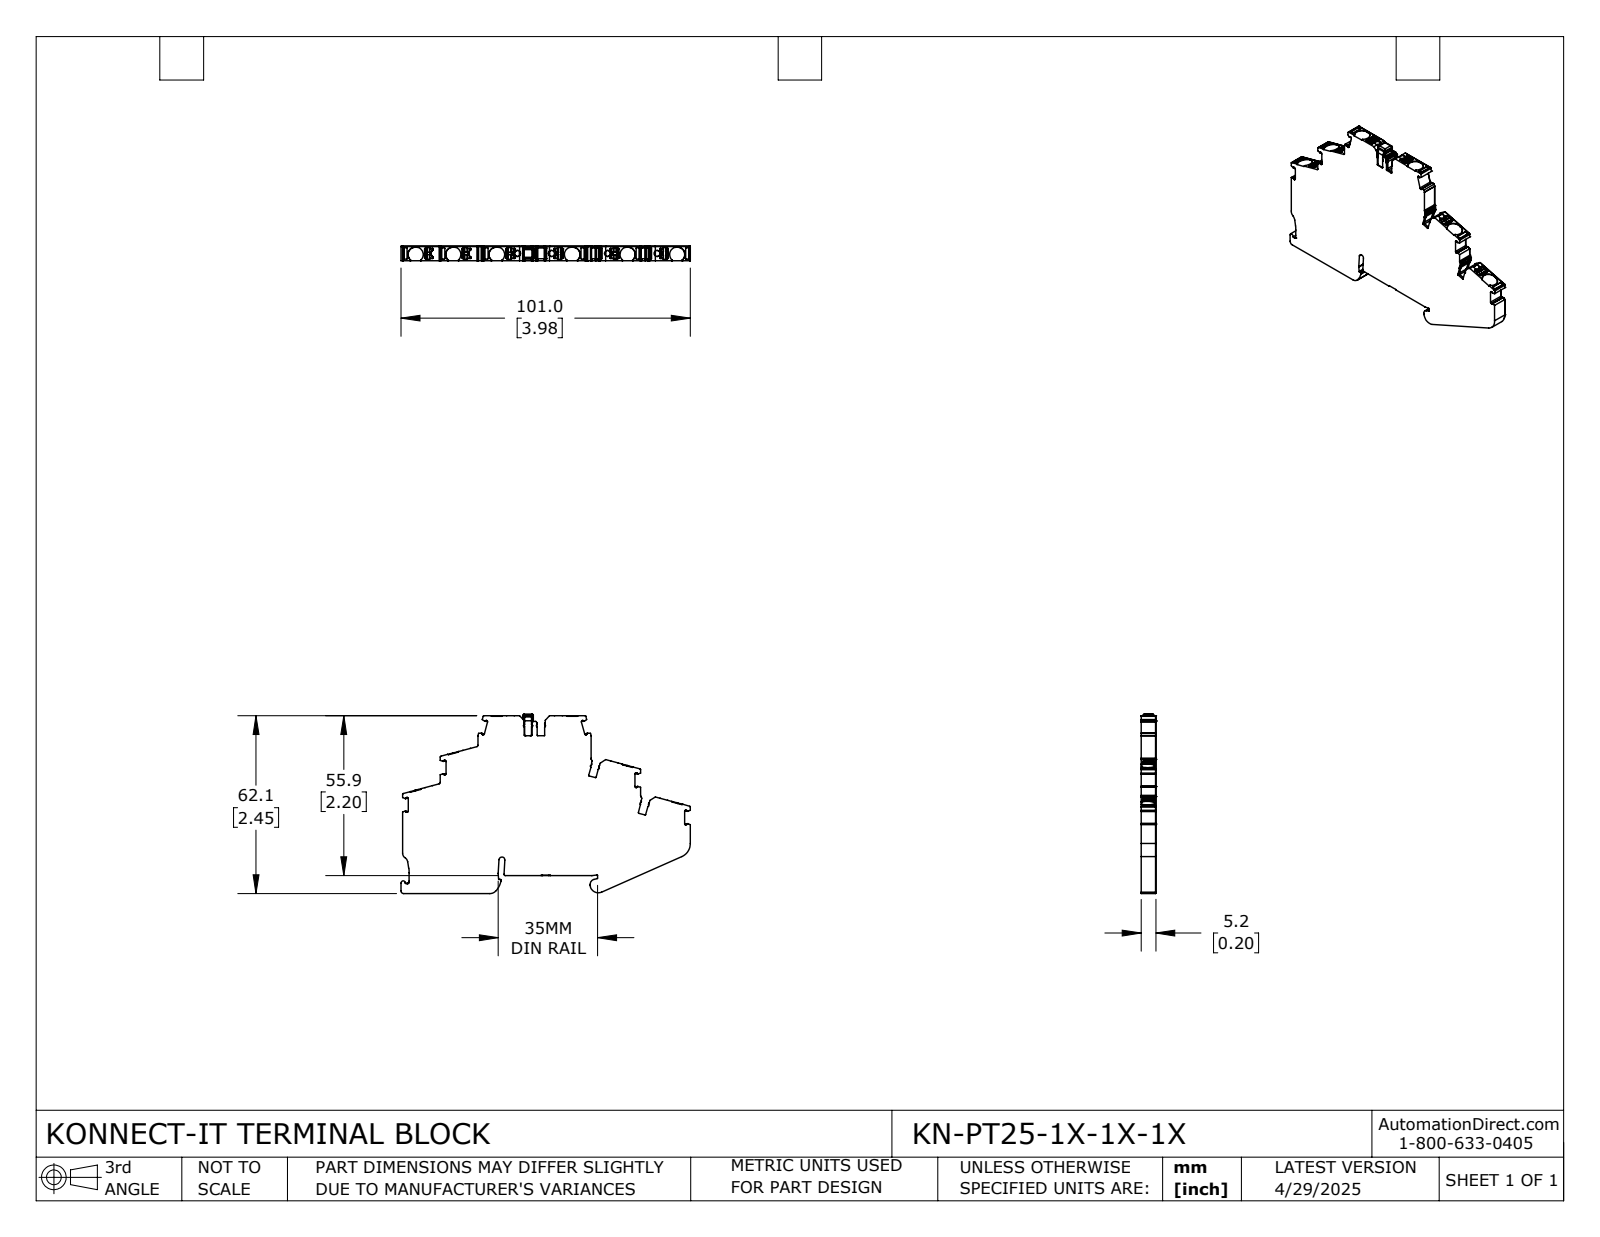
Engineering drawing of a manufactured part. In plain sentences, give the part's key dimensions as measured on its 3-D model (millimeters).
The part is named "KN-PT25-1X-1X-1X". Its 3-D file was written by "SolidWorks 2024 (CONFIG_CONTROL_DESIGN)". It is 1 solid with 1314 faces: 638 planar, 565 cylindrical and 111 other. Overall it measures 101 by 62.7 by 5.2 millimeters. Its volume is 22 290 cubic millimeters and its surface area 10 910 square millimeters. Round holes: 4 of diameter 2.1. Partial cylindrical surfaces (rounded edges, fillets, slot ends): 132 of radius 0.2, 51 of radius 0.3, 49 of radius 0.1, 34 of radius 0.5, 24 of radius 0.2, 17 of radius 0.4, 14 of radius 0.6, 12 of radius 0.2. The main face-to-face distances are 5.2, 6.2, 2, 55.7, 61.9, 8.1, 17.3, 13.2, 55.9, 62.1. The hole center spacings are 11.8, 20.1.
